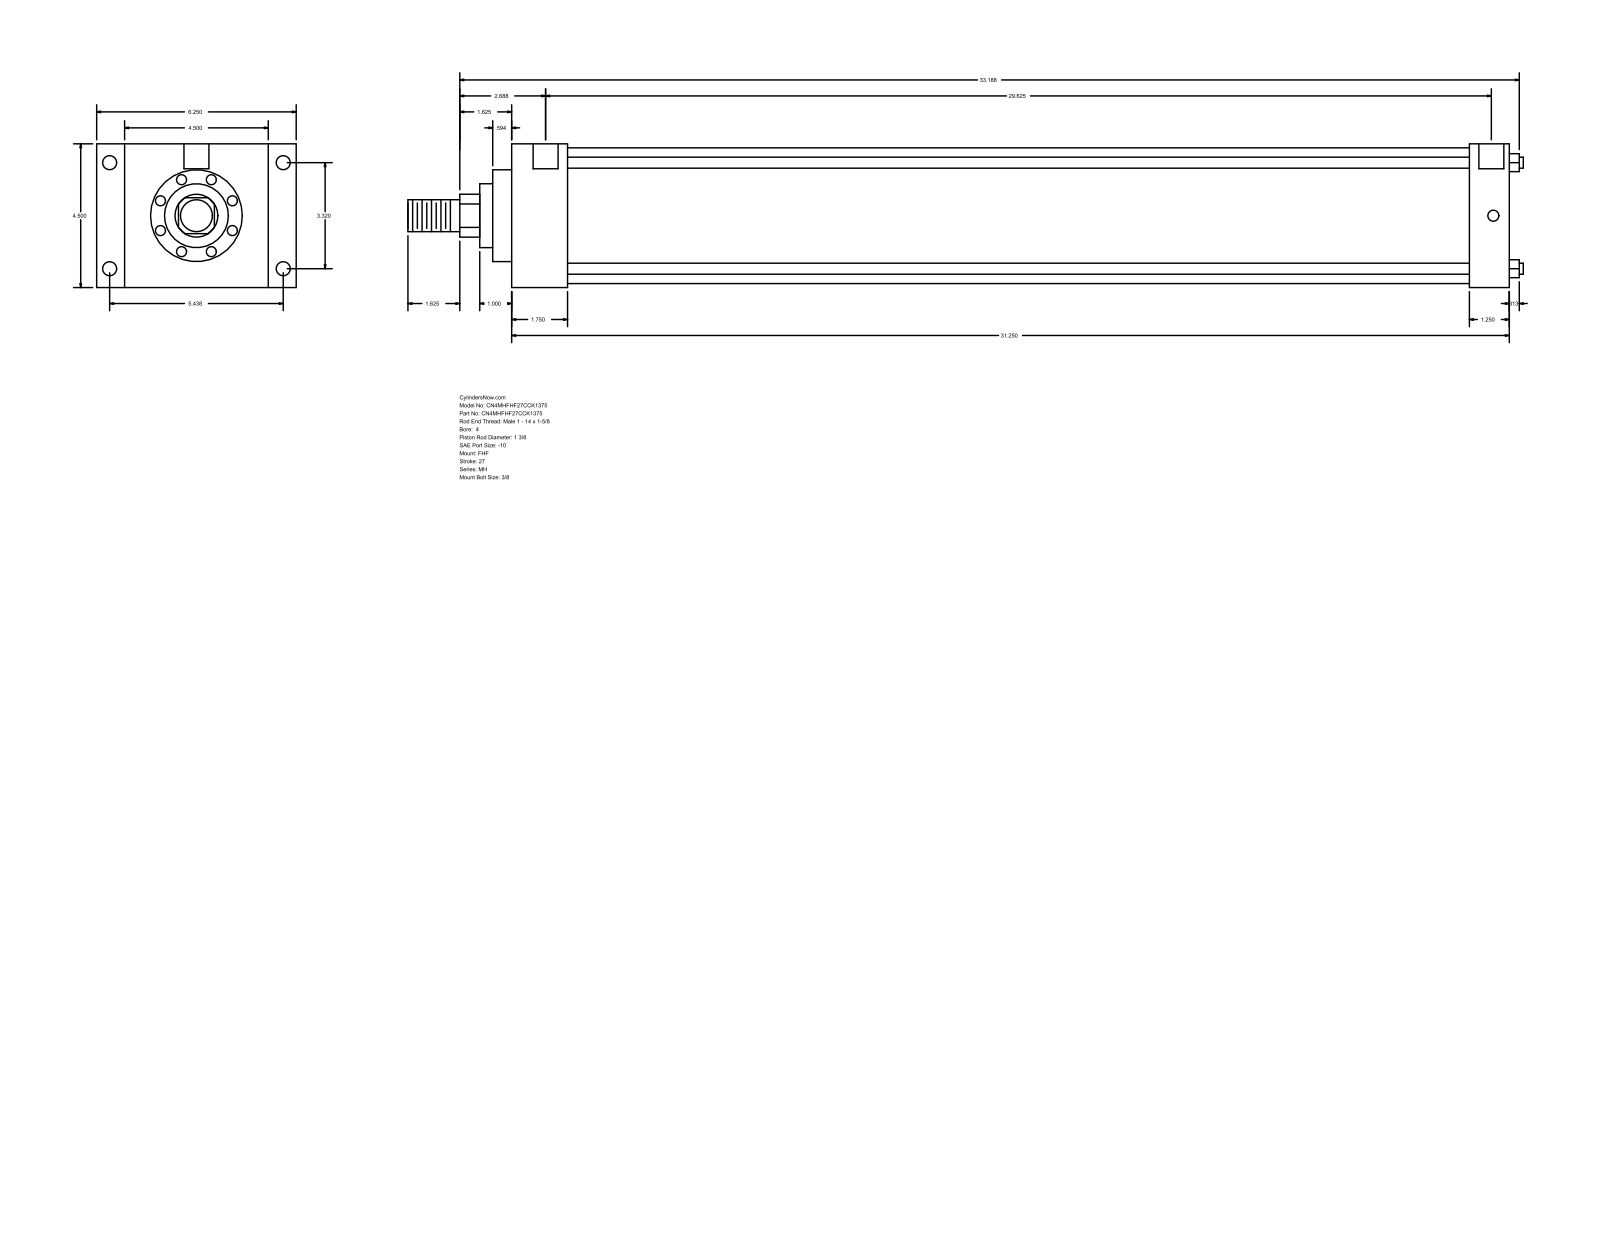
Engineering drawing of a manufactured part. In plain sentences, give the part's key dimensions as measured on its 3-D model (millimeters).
The part is named "MH_FHF__0400_1.375". Its 3-D file was written by "GSSL Pune (CONFIG_CONTROL_DESIGN)". It is 0 solids with 90 faces: 61 planar, 29 cylindrical and 0 other. Overall it measures 887.41 by 158.75 by 114.3 millimeters. Round holes: 4 of diameter 8.73, 4 of diameter 11.13, 2 of diameter 19.84. Round bosses or shafts: 4 of diameter 8.76, 1 of diameter 107.95, 1 of diameter 73.03, 1 of diameter 50.8, 1 of diameter 34.92, 1 of diameter 25.4. Partial cylindrical surfaces (rounded edges, fillets, slot ends): 1 of radius 17.06. The main face-to-face distances are 114.3, 793.75, 44.45, 749.3, 22.23, 136.53, 158.76, 762, 717.55, 31.75. The hole center spacings are 1.59, 84.32, 138.12, 161.82, 754.07, 755.66, 752.48.
